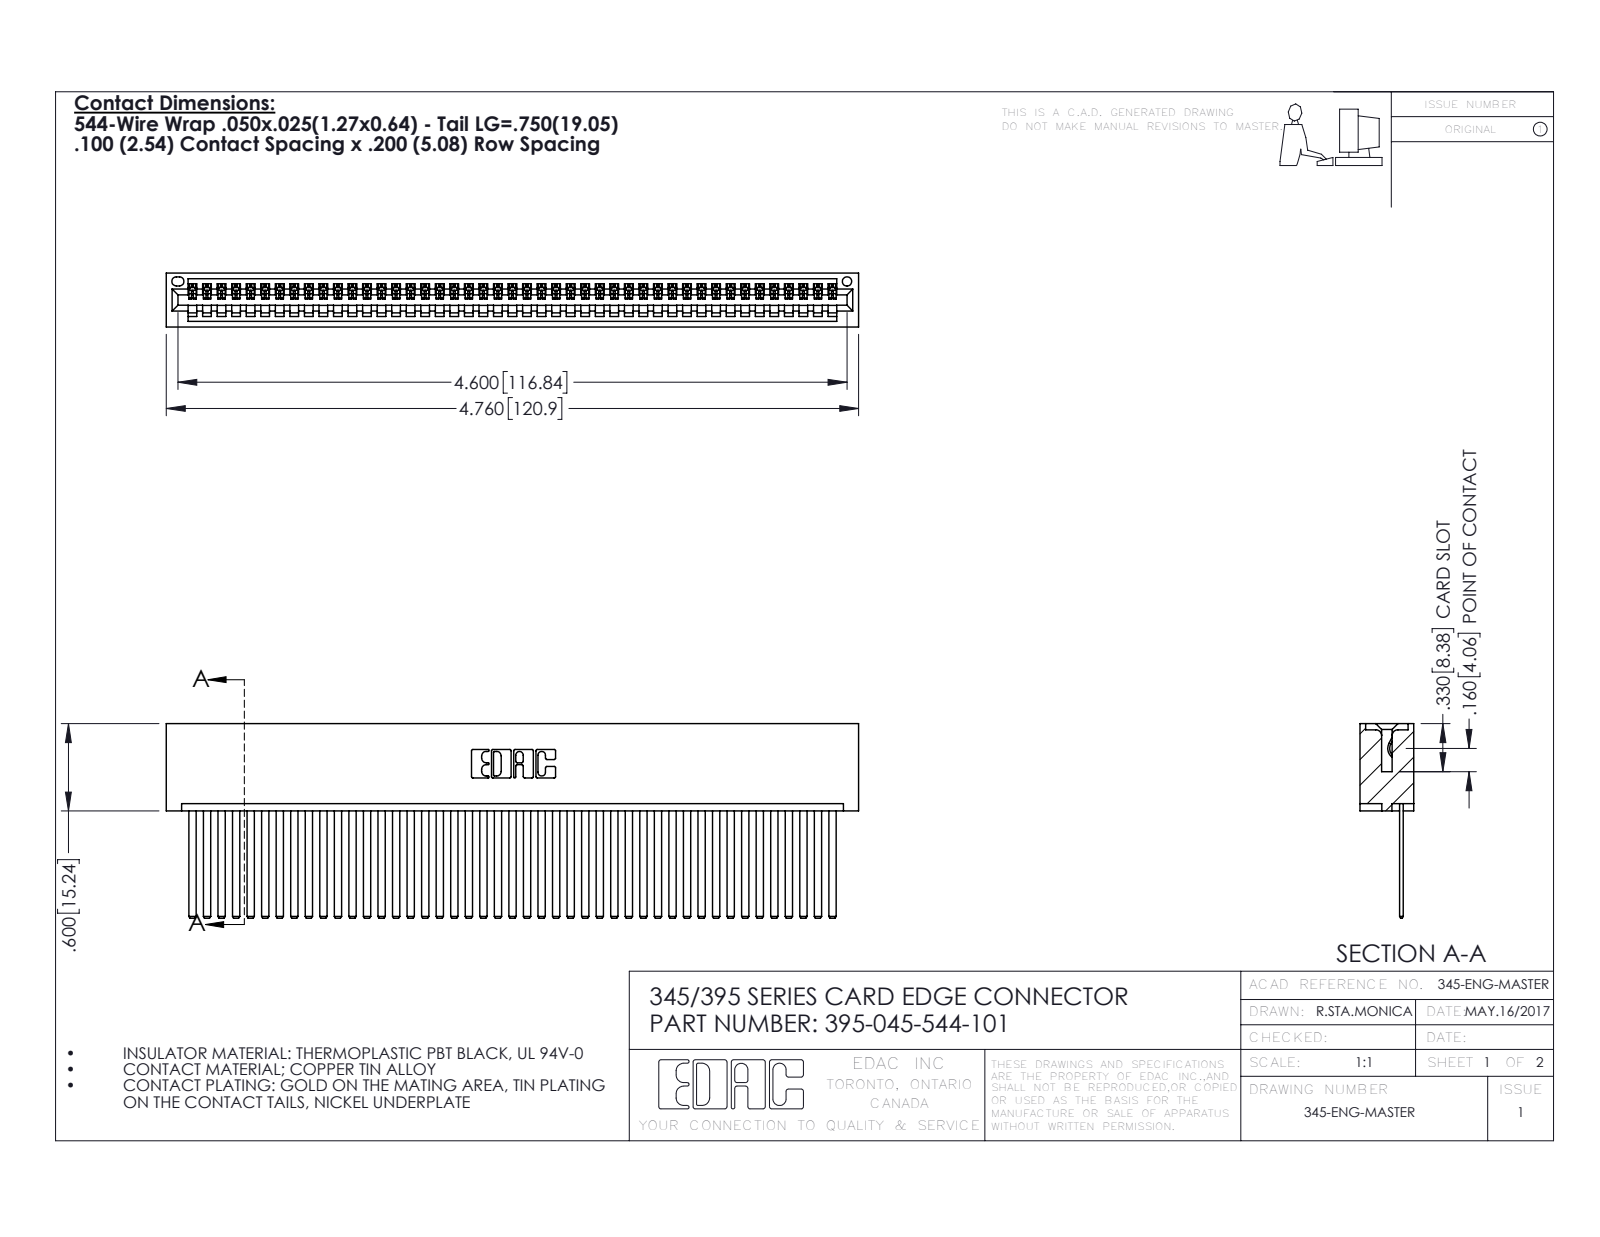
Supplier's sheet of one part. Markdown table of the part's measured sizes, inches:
| quantity | value |
| --- | --- |
| part name | 345-292-001_345-293-144; 395-045-544-101; 345 Part_No Mounting Lugs |
| STEP written by | SolidWorks 2016 (CONFIG_CONTROL_DESIGN) |
| units | inches |
| bodies | 46 solids, 2458 faces (1696 planar, 762 cylindrical, 0 other) |
| overall size | 4.76 × 1.337 × 0.37 |
| volume | 0.77 in³ |
| surface area | 28.76 in² |
| round holes (diameter × count) | 0.064 × 1 |
| partial cylindrical surfaces (radius × count) | 0.006 × 90, 0.01 × 22, 0.007 × 6, 0.031 × 6, 0.026 × 3, 0.031 × 2, 0.04 × 2, 0.014 × 1 |
| main face-to-face distances | 0.072, 0.298, 0.025, 0.098, 0.272, 0.37, 0.2, 0.225, 0.149, 0.072 |
